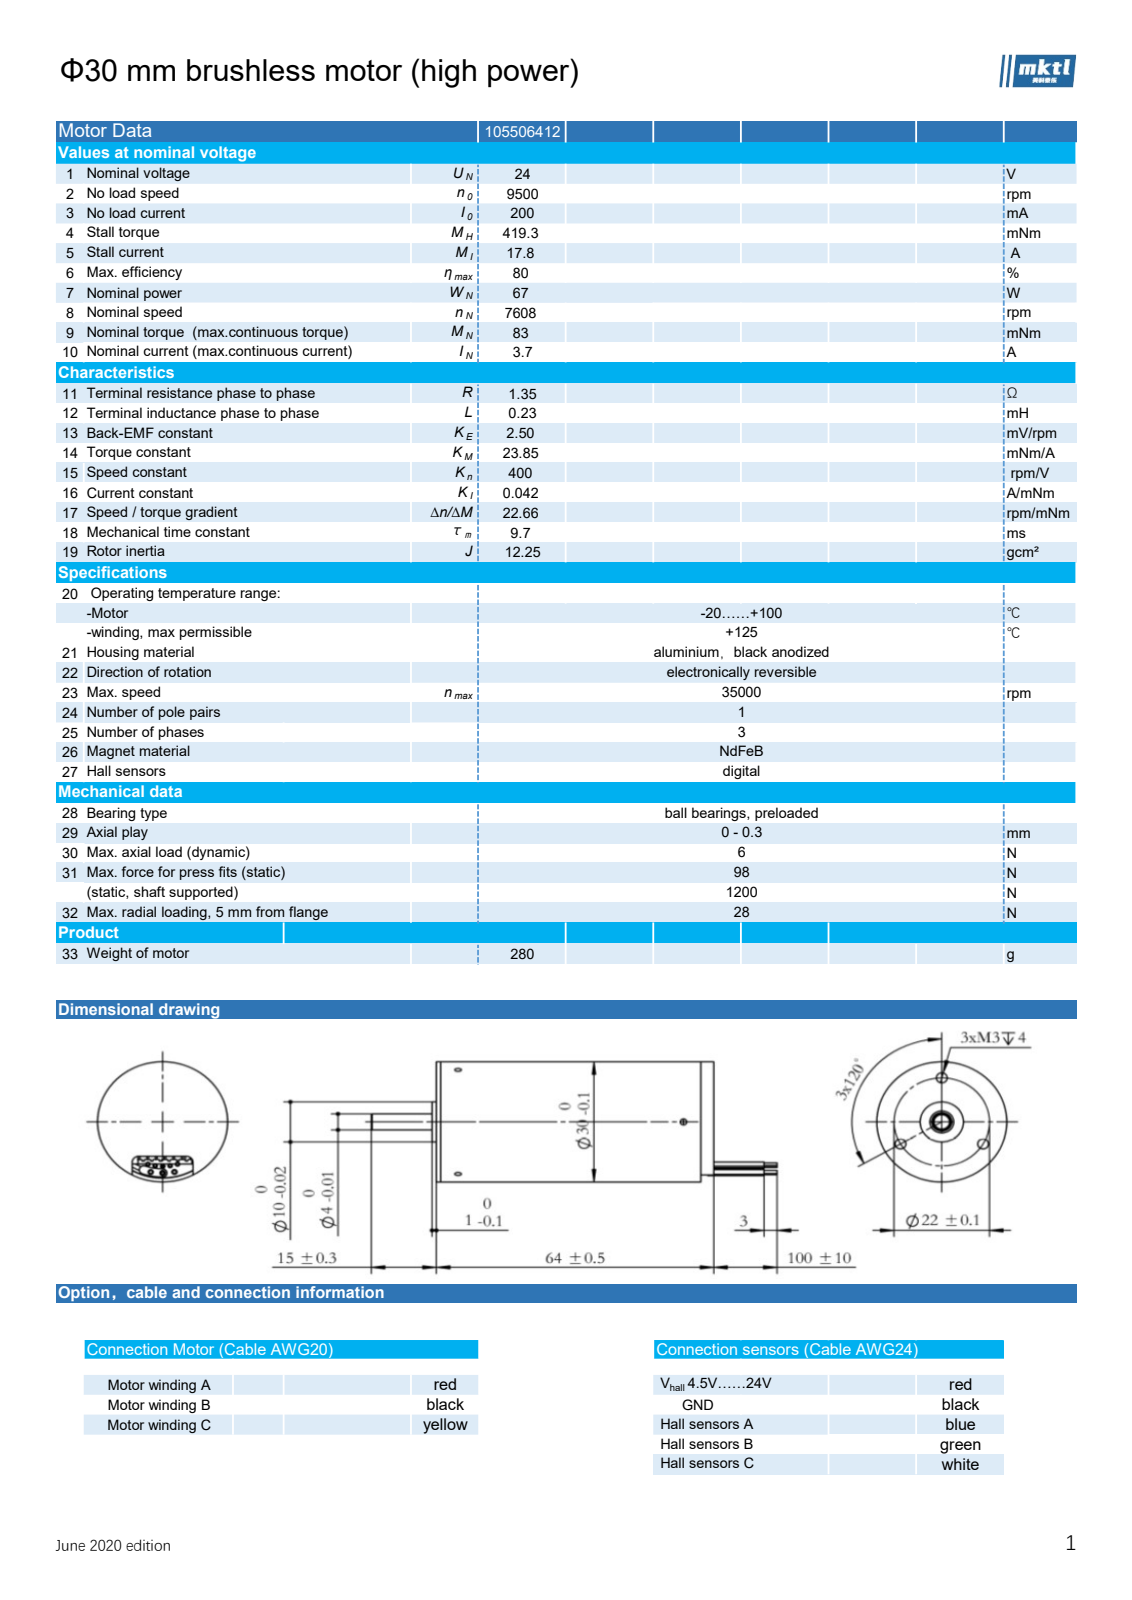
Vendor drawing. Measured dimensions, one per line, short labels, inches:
name: 端线接线板(带线) 105506412.1; 霍尔控制线(黑色) 105506412.1; 混合胶 105506412.1; 电机电源线(黑色) 105506412.1 (+8 more)
written by: SolidWorks 2018 (CONFIG_CONTROL_DESIGN)
unit: in
bodies: 29 solids, 446 faces (121 planar, 239 cylindrical, 86 other)
size: 3.795 × 1.181 × 1.181
volume: 0.881 in³; area: 30.67 in²
holes: 6× ⌀0.063, 5× ⌀0.044, 3× ⌀0.051, 3× ⌀0.098, 2× ⌀0.071, 1× ⌀0.315, 1× ⌀0.512, 1× ⌀0.587, 1× ⌀0.945
bosses: 15× ⌀0.039, 10× ⌀0.031, 3× ⌀0.071, 3× ⌀0.055, 3× ⌀0.047, 2× ⌀0.063, 1× ⌀1.181, 1× ⌀1.106
rounds: 2× R0.059
face distances: 2.52, 0.197, 2.224, 0.256, 2.264, 0.039, 0.118, 0.236, 2.48, 2.283
hole spacings: 0.079, 0.157, 0.433, 0.453, 0.819, 0.931, 0.02, 0.087
